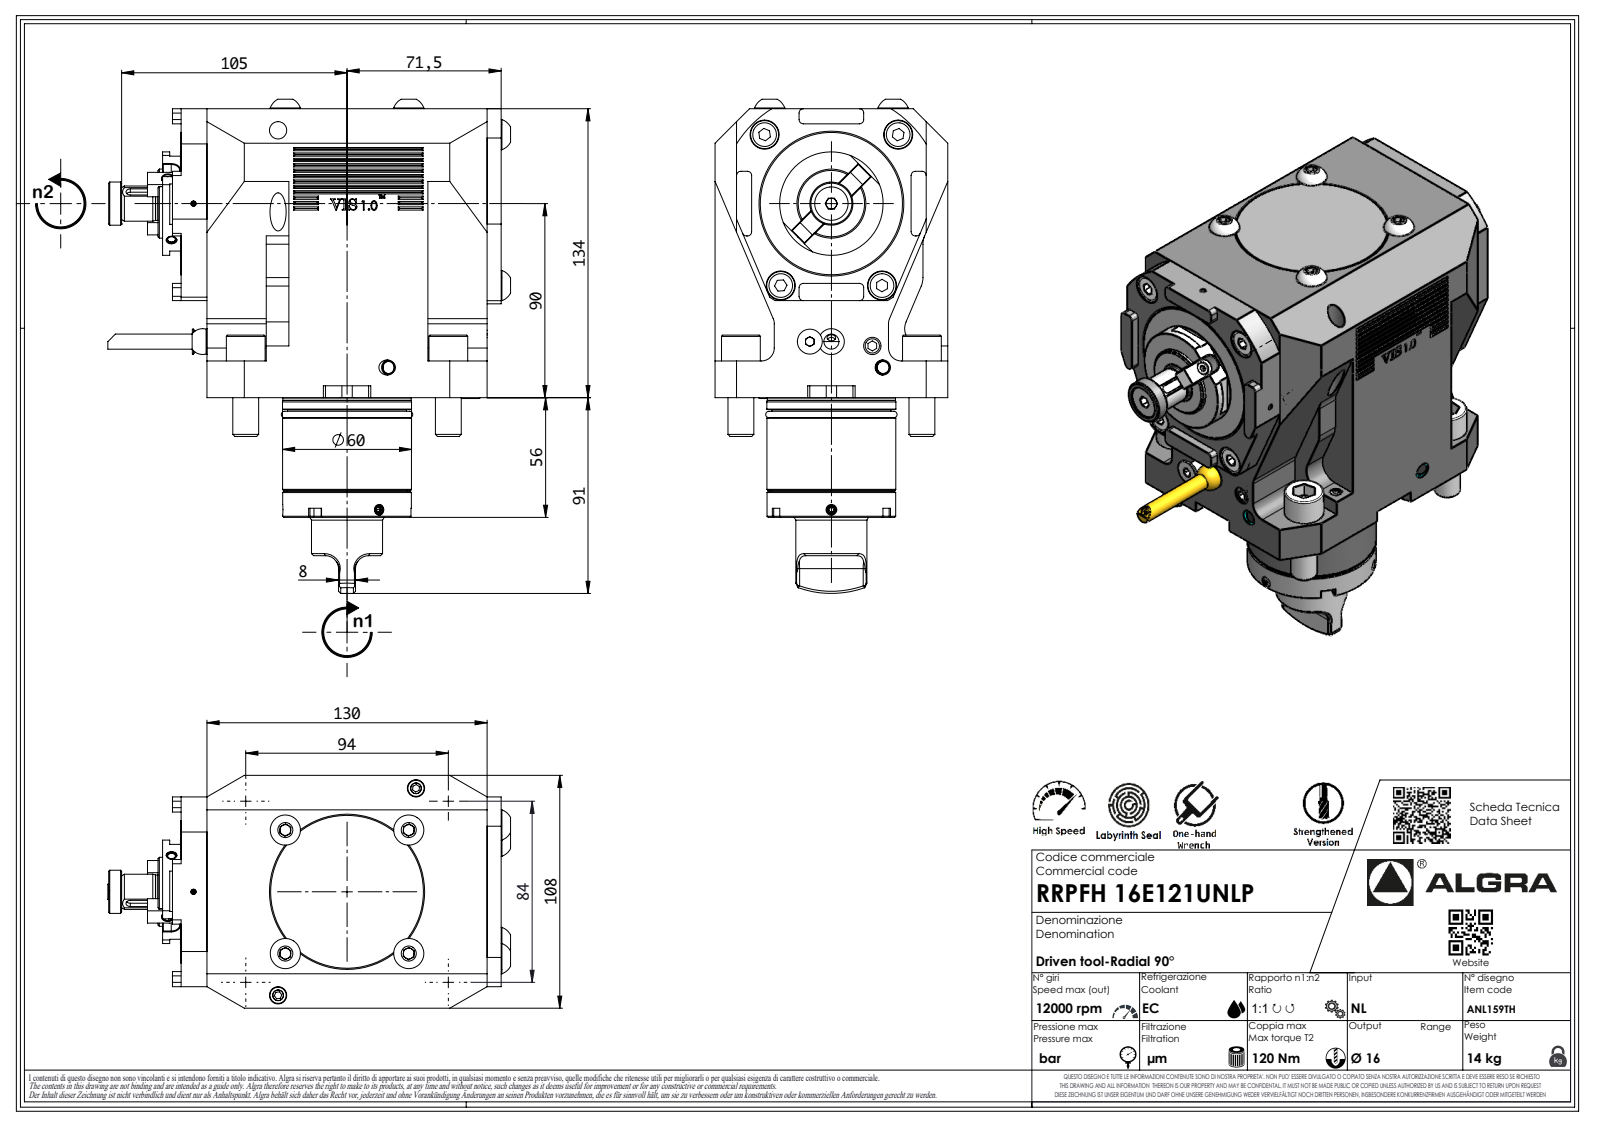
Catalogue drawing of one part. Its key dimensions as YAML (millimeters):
part_name: "RRPFH16E121UNLP"
step_written_by: "SolidWorks 2023 (AUTOMOTIVE_DESIGN)"
units: millimeters
bodies: {solids: 1, faces: 1019, planar: 708, cylindrical: 137, other: 174}
overall_size: [224.8, 182.5, 108]
volume: 2002000
surface_area: 126887
round_holes:
  - {diameter: 2.1, count: 1}
round_bosses_or_shafts:
  - {diameter: 18, count: 4}
  - {diameter: 12, count: 4}
  - {diameter: 59.9, count: 1}
  - {diameter: 59.8, count: 1}
  - {diameter: 59.7, count: 1}
  - {diameter: 59.5, count: 1}
  - {diameter: 55.2, count: 1}
  - {diameter: 48, count: 1}
partial_cylinders:
  - {radius: 0.2, count: 21}
  - {radius: 8, count: 18}
  - {radius: 2, count: 16}
  - {radius: 6, count: 10}
  - {radius: 0.33, count: 7}
  - {radius: 0.52, count: 7}
  - {radius: 3.7, count: 7}
  - {radius: 10, count: 4}
face_to_face_distances: [108, 134, 27.5, 12, 102.5, 6.5, 136.5, 5.5, 148.5, 39.5]
